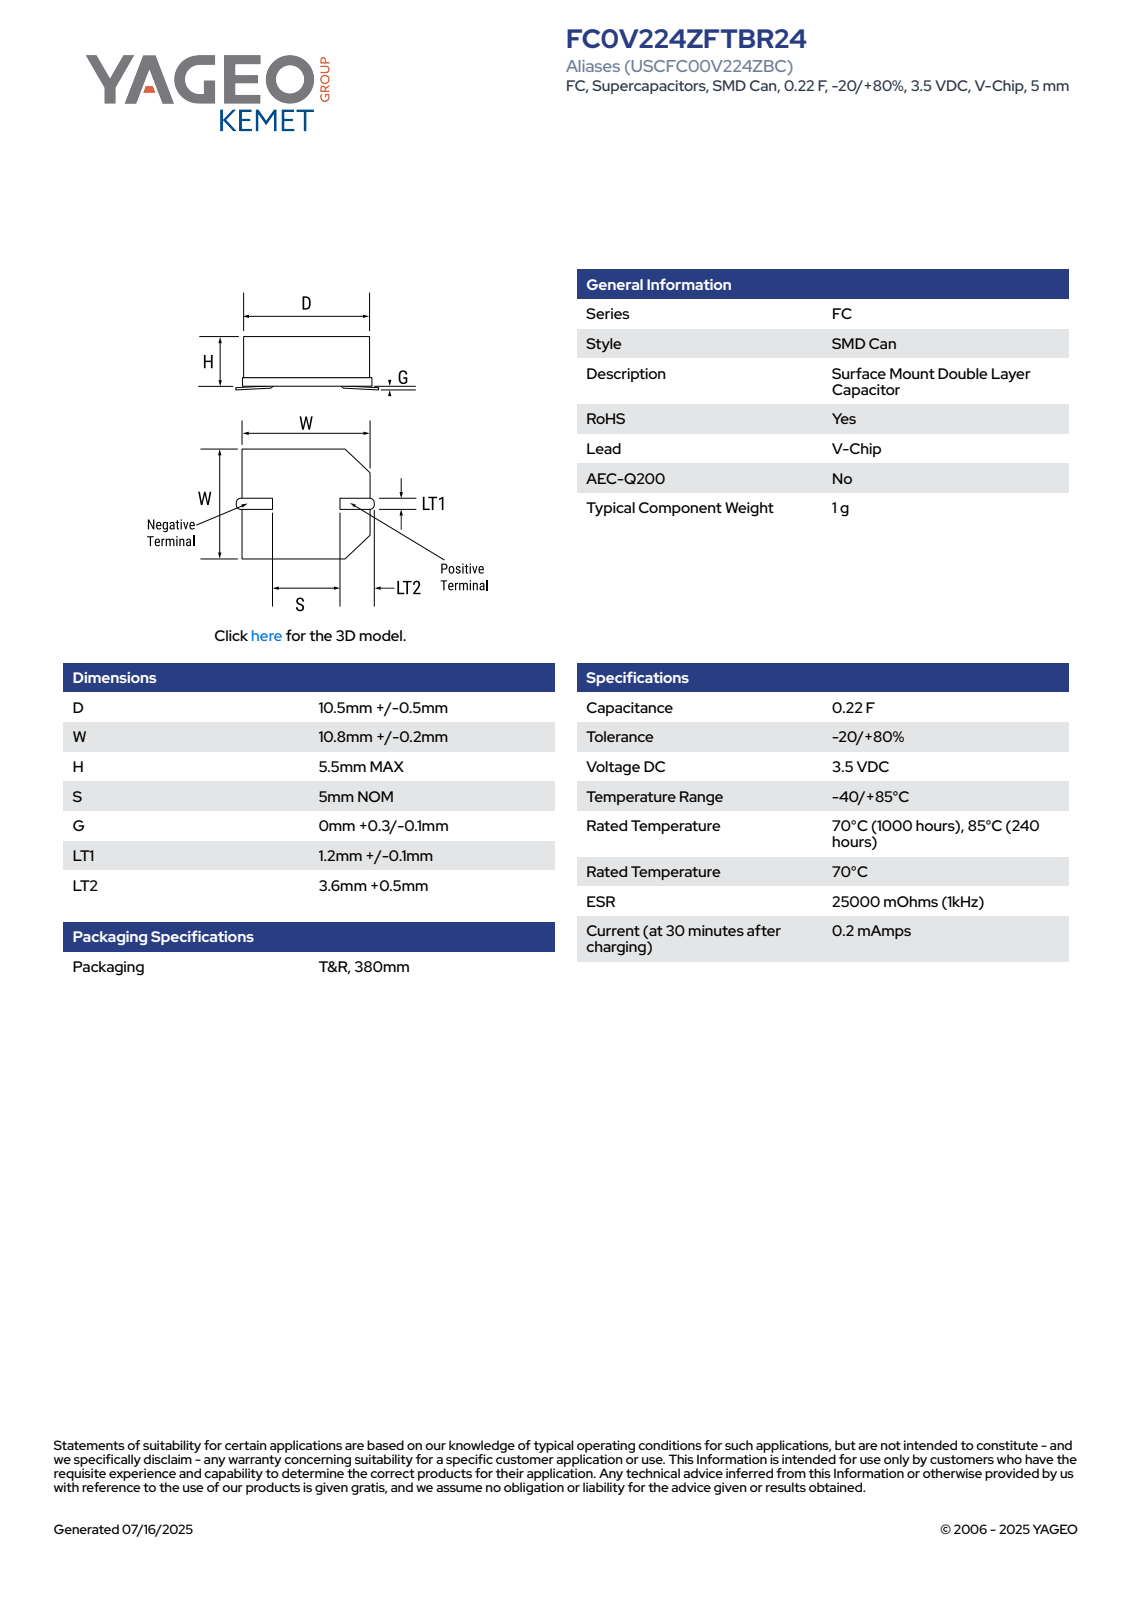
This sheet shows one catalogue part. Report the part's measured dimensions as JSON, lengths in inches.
{"part_name": "CDC_VC_D10.5L5.5LT11.3G0.3W11LT24.1", "step_written_by": "SolidWorks 2014 (AUTOMOTIVE_DESIGN)", "units": "inches", "bodies": {"solids": 5, "faces": 60, "planar": 49, "cylindrical": 5, "other": 6}, "overall_size": [0.52, 0.433, 0.217], "volume_in3": 0.03, "surface_area_in2": 0.944, "round_bosses_or_shafts": [[0.413, 1]], "partial_cylinders_radius": [[0.008, 2], [0.164, 1]], "face_to_face_distances": [0.054, 0.205, 0.15, 0.433, 0.217, 0.066, 0.191, 0.242, 0.051, 0.043]}
